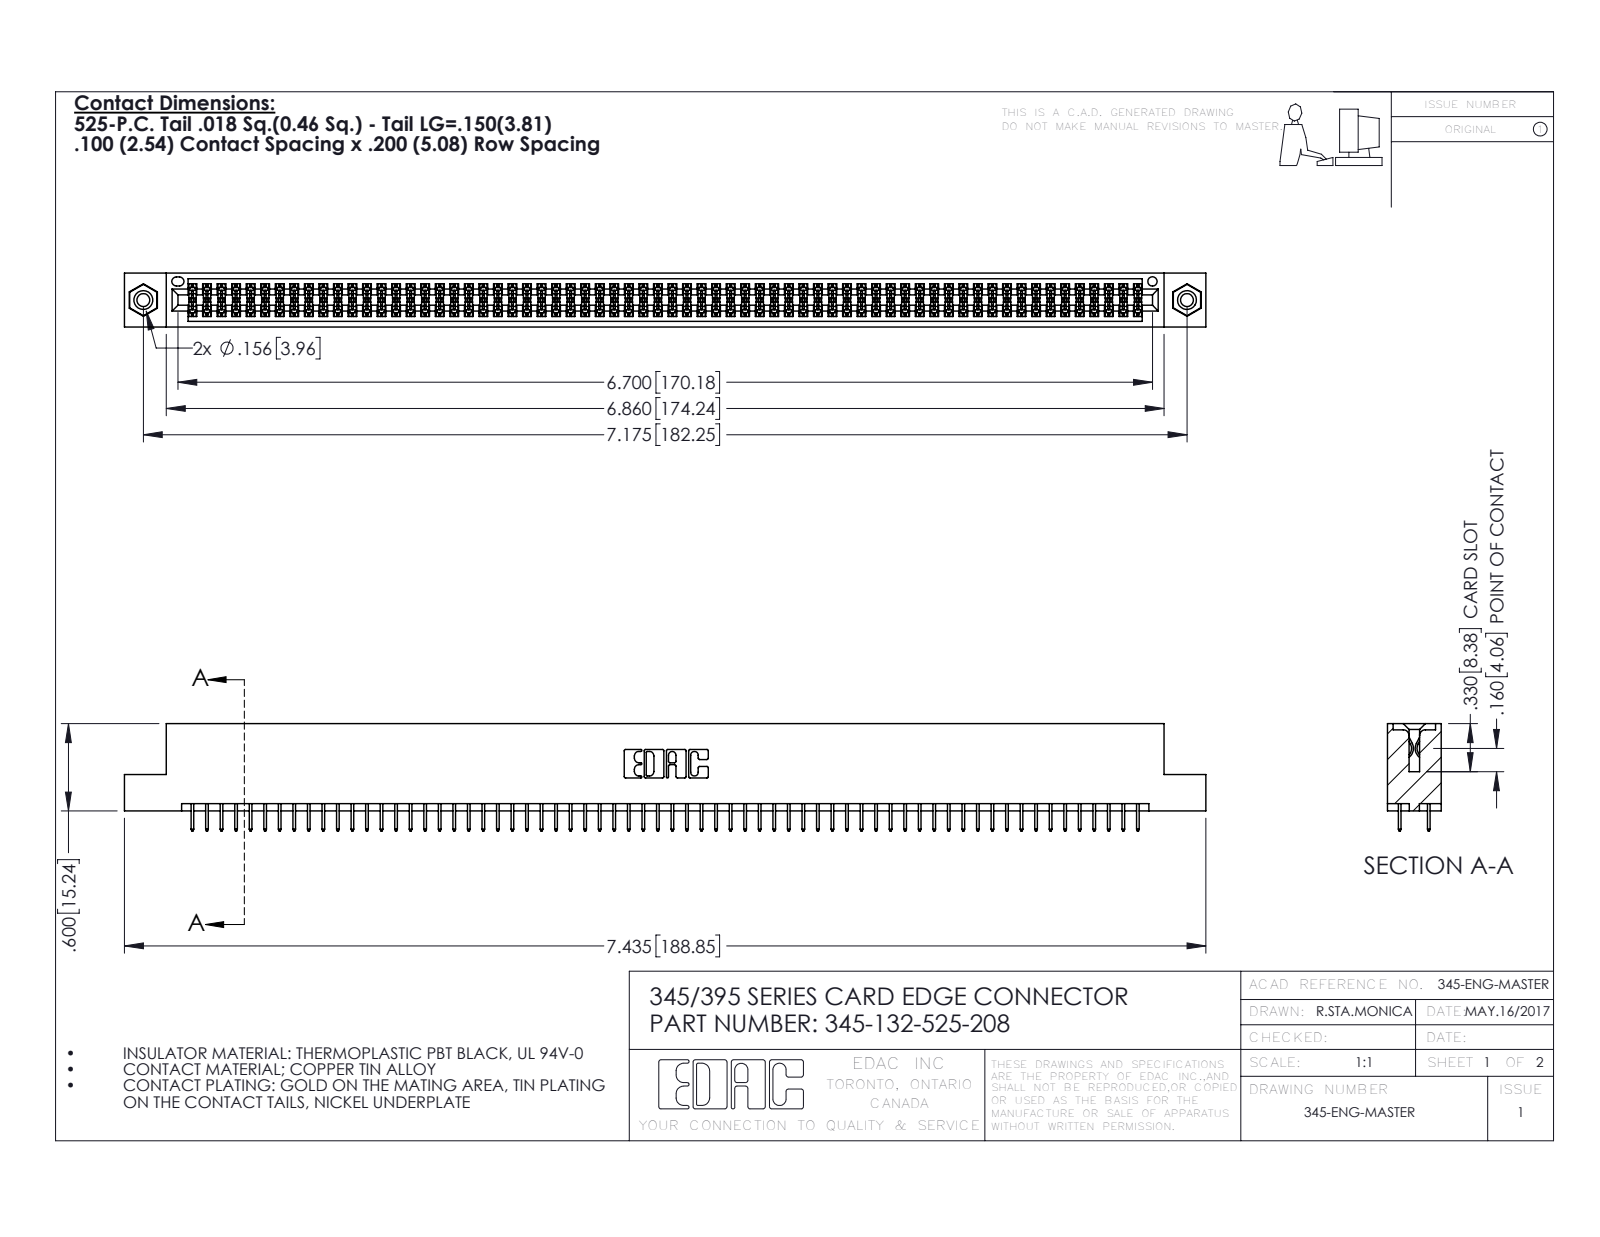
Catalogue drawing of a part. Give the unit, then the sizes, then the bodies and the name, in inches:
Units: inches
Overall size (bounding box): 7.435 × 0.737 × 0.37
Round holes (diameter × count): ⌀0.089 ×2, ⌀0.125 ×2, ⌀0.156 ×2, ⌀0.064 ×1
Round bosses / shafts (diameter × count): ⌀0.155 ×2
Partial cylindrical surfaces — rounded edges, fillets, slot ends (radius × count): R0.006 ×264, R0.01 ×22, R0.007 ×6, R0.031 ×6, R0.026 ×3, R0.014 ×2, R0.019 ×2, R0.022 ×2
Main face-to-face distances: 0.072, 0.298, 0.2, 0.37, 0.098, 0.272, 0.025, 0.225, 0.072, 0.175
Hole centre spacings: 0.27, 6.939, 7.175
Volume: 1.119 in³ · Surface area: 41.76 in²
Bodies: 135 solids, 7314 faces (5260 planar, 2038 cylindrical, 16 other)
Part name (STEP PRODUCT): 345 Part_Flush Mounting Lugs - 0.156 Dia-TI; 345-292-001_345-293-125; 345-250-001_345-250-003-102; 345-132-525-208
STEP written by: SolidWorks 2020 (CONFIG_CONTROL_DESIGN)
